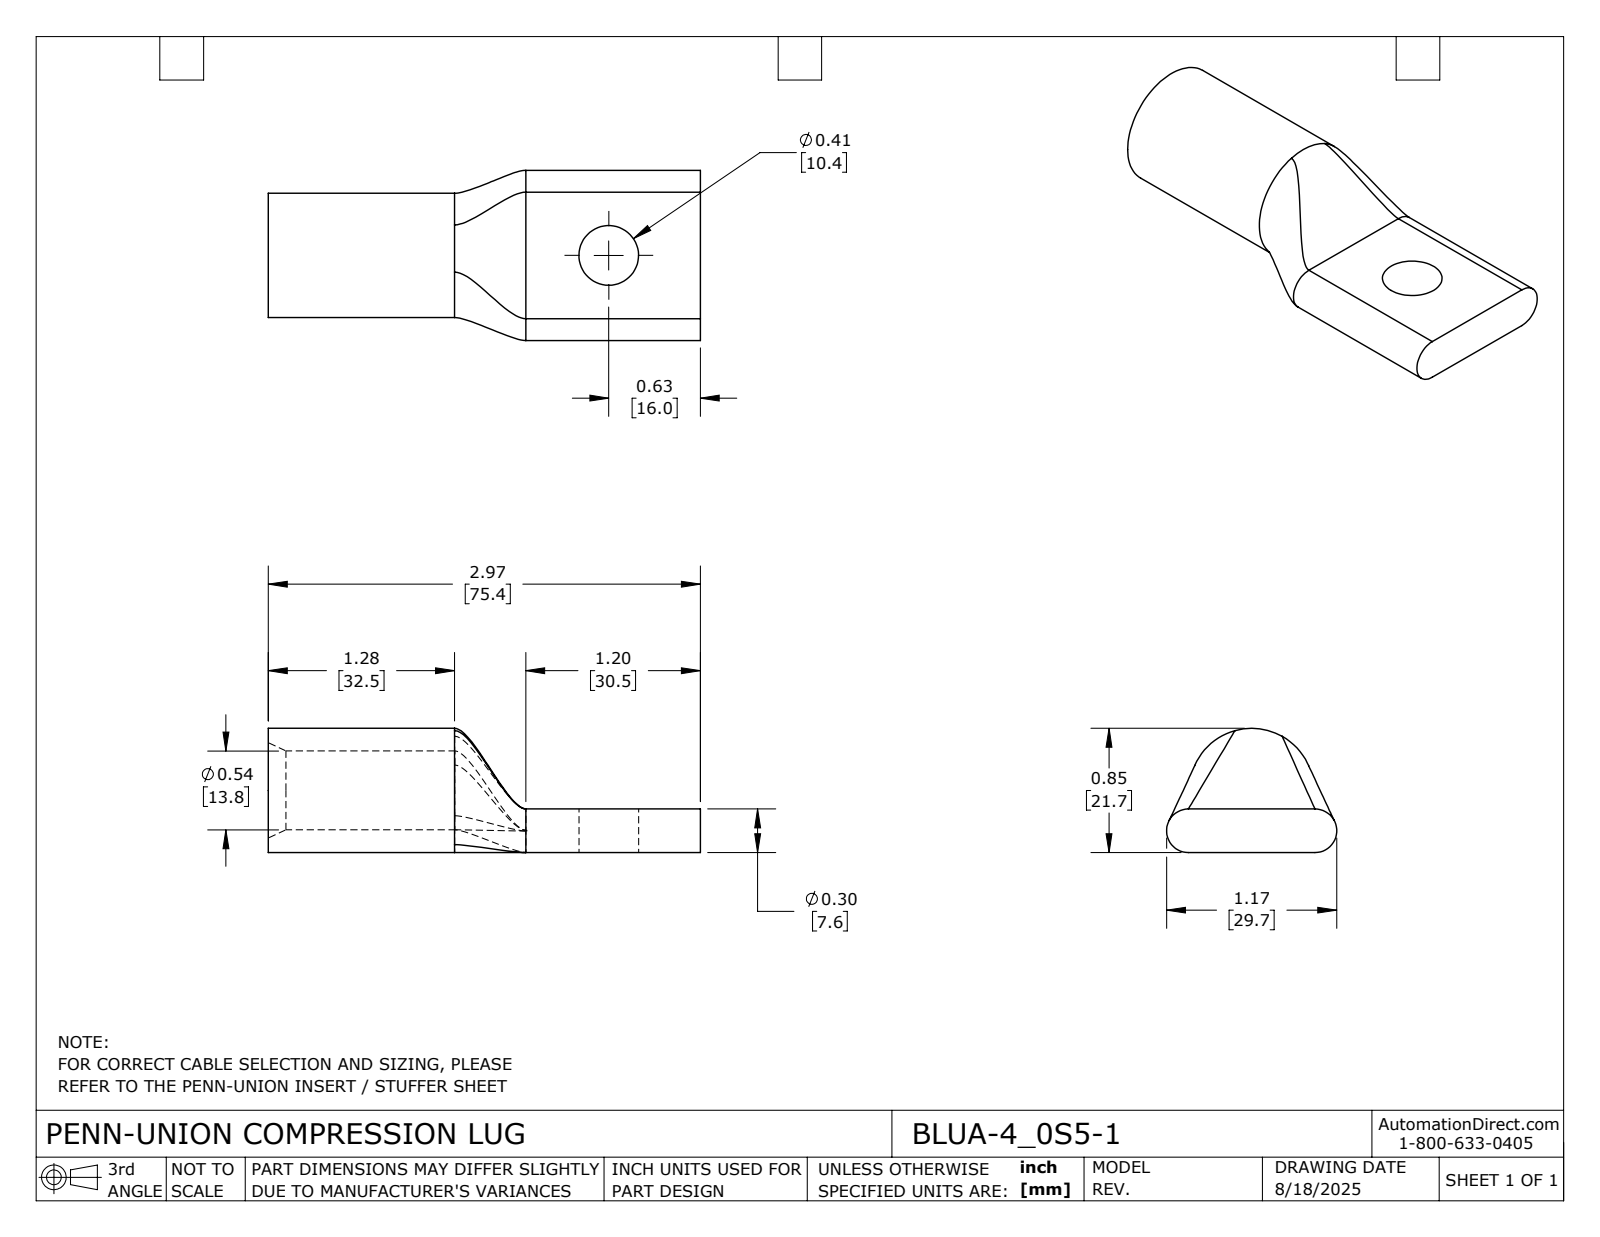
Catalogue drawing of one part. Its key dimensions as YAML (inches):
part_name: "BLUA-4_0S5-1"
step_written_by: "SolidWorks 2024 (CONFIG_CONTROL_DESIGN)"
units: inches
bodies: {solids: 1, faces: 24, planar: 5, cylindrical: 9, other: 10}
overall_size: [2.97, 1.17, 0.854]
volume: 0.954
surface_area: 12.08
round_holes:
  - {diameter: 0.41, count: 1}
  - {diameter: 0.542, count: 1}
round_bosses_or_shafts:
  - {diameter: 0.854, count: 1}
partial_cylinders:
  - {radius: 0.15, count: 2}
face_to_face_distances: [0.3, 2.97, 1.77, 1.2]
